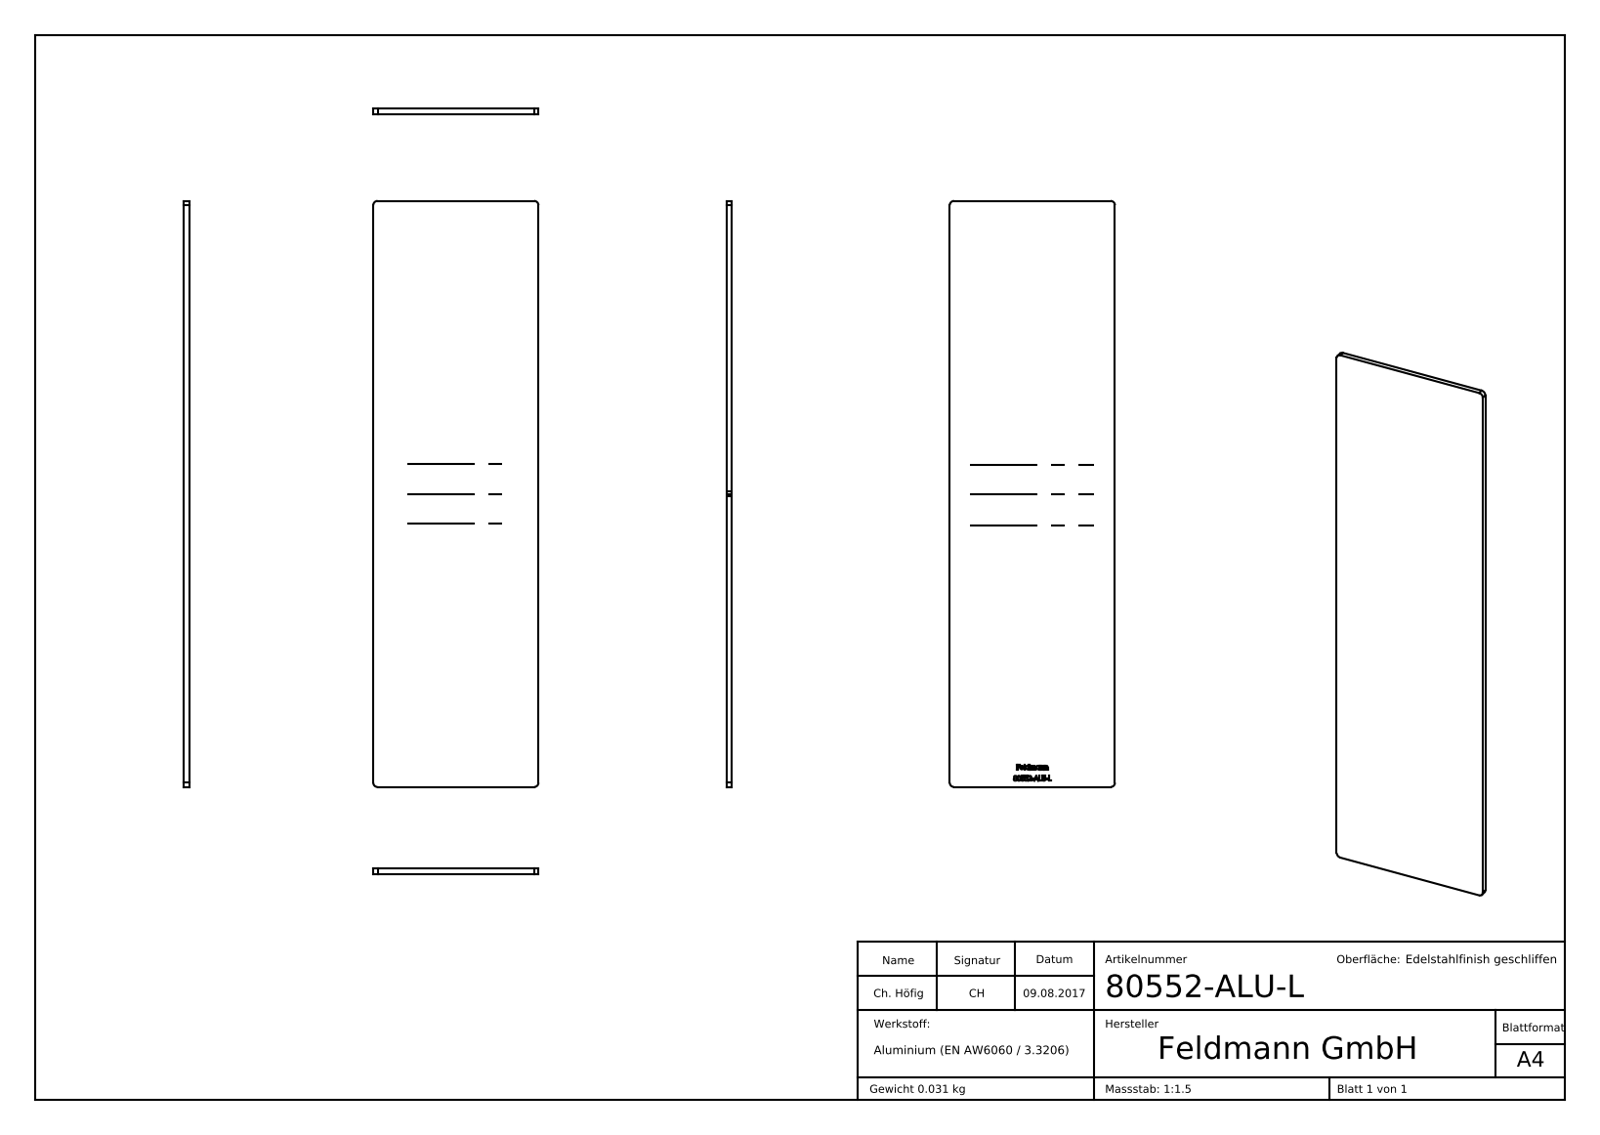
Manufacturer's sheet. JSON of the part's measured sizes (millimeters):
{"part_name": "80552-ALU-L", "step_written_by": "SolidWorks 2015 (CONFIG_CONTROL_DESIGN)", "units": "millimeters", "bodies": {"solids": 1, "faces": 248, "planar": 141, "cylindrical": 4, "other": 103}, "overall_size": [165, 46.5, 1.5], "volume_mm3": 11506, "surface_area_mm2": 15984, "partial_cylinders_radius": [[1.2, 4]], "face_to_face_distances": [1.5, 46.5, 165, 1.4, 1.19, 1.8, 5.62, 2.98, 4.23, 2.64]}
